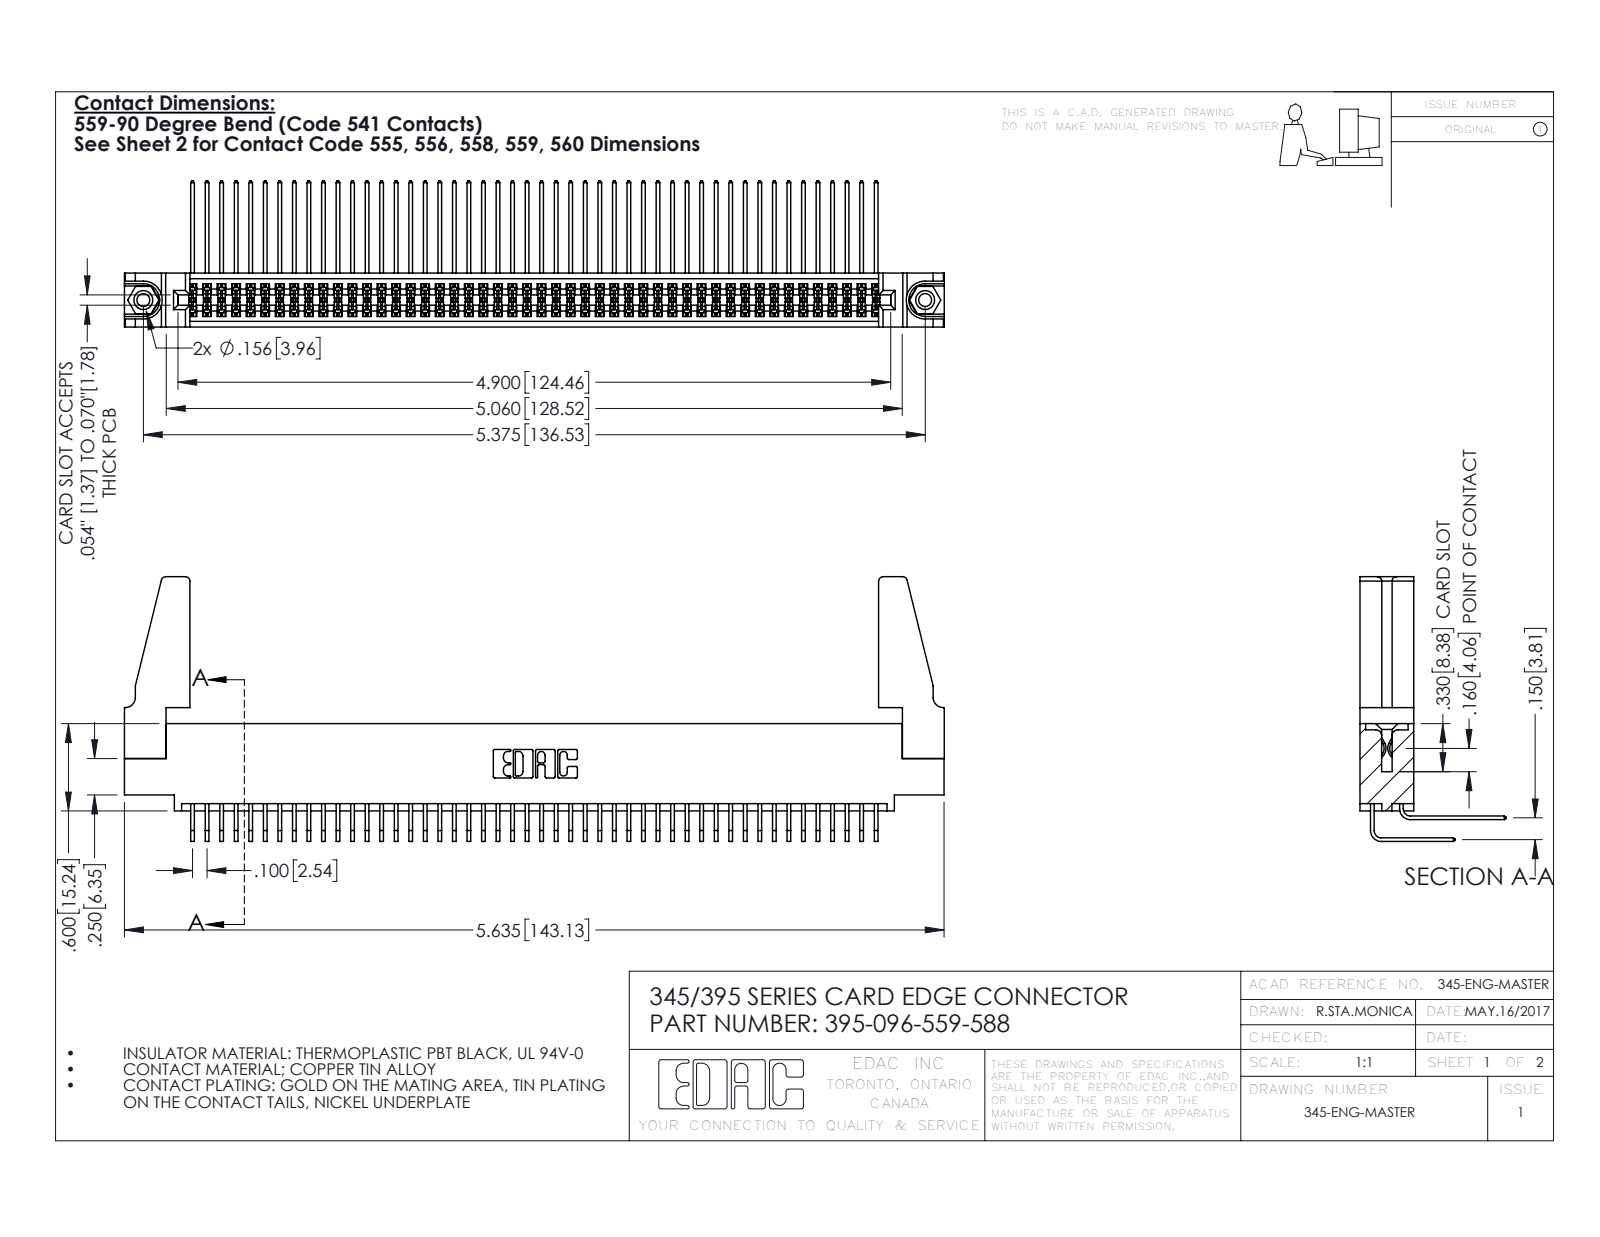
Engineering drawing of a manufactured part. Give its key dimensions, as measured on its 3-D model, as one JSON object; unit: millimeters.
{"part_name": "395-096-559-588; 345-292-001_559 Tail - 2; 345-292-001_558 559 Tail - 1; 345-250-001_345-250-001-102 (+2 more)", "step_written_by": "SolidWorks 2016 (CONFIG_CONTROL_DESIGN)", "units": "millimeters", "bodies": {"solids": 101, "faces": 5246, "planar": 3516, "cylindrical": 1714, "other": 16}, "overall_size": [143.2, 46.2, 25.5], "volume_mm3": 17700, "surface_area_mm2": 27280, "round_holes": [[2.3, 2], [3.2, 2], [4, 2], [1.6, 1]], "round_bosses_or_shafts": [[3.9, 2]], "partial_cylinders_radius": [[0.2, 145], [0.3, 22], [0.8, 8], [0.2, 6], [0.8, 6], [0.7, 3], [0.4, 2], [0.5, 2]], "face_to_face_distances": [1.8, 7.6, 9.4, 5.1, 2.5, 6.9, 0.6, 5.7, 4.4, 3.8], "hole_center_spacings": [6.9, 130.5, 136.5]}
